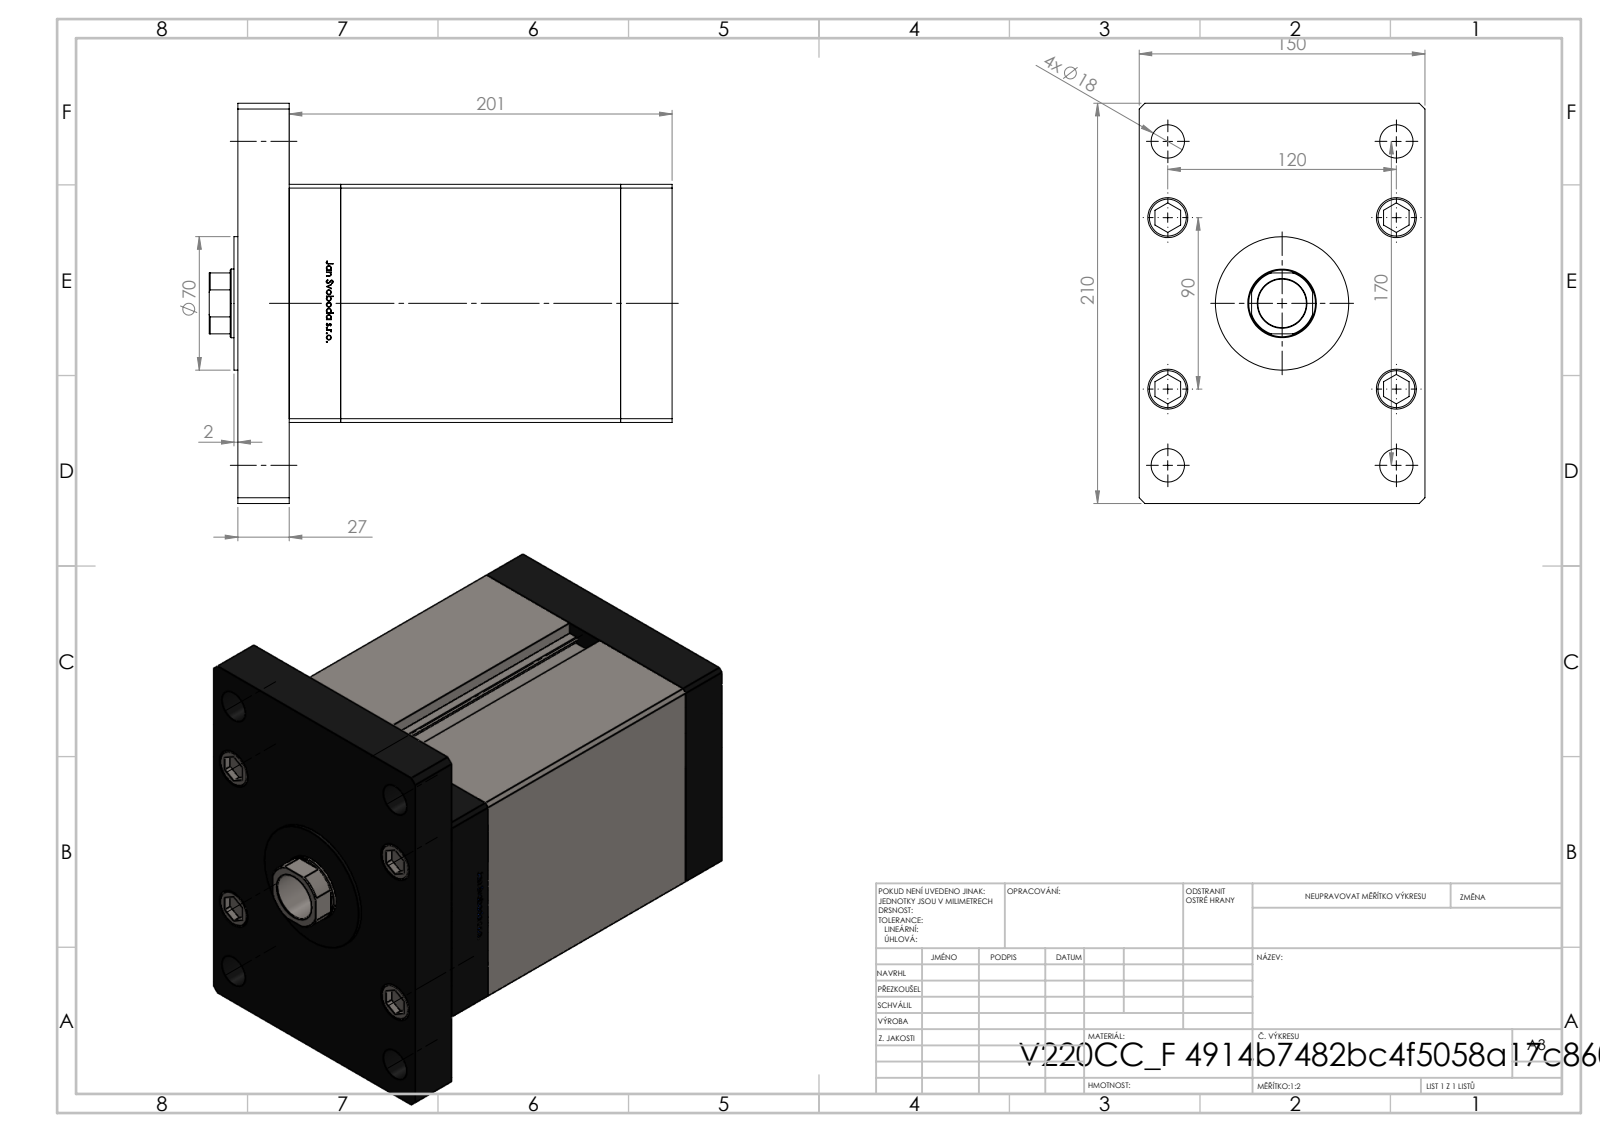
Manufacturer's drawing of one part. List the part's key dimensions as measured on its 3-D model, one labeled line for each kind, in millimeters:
Part name (STEP PRODUCT): V220C_F_MIDDLE; V220C_VC_F; V220C_FRONT_F; ALLEN BOLT (+2 more)
STEP written by: SolidWorks 2019 (CONFIG_CONTROL_DESIGN)
Units: millimetres
Bodies: 19 solids, 1298 faces (513 planar, 179 cylindrical, 606 other)
Overall size (bounding box): 243 × 210 × 150
Volume: 4 076 000 mm³ · Surface area: 452 115 mm²
Round holes (diameter × count): ⌀17.5 ×9, ⌀22 ×5, ⌀16 ×4, ⌀21 ×4, ⌀25.5 ×1, ⌀36 ×1, ⌀37.5 ×1
Round bosses / shafts (diameter × count): ⌀8 ×9, ⌀21 ×5, ⌀80 ×1, ⌀70 ×1
Partial cylindrical surfaces — rounded edges, fillets, slot ends (radius × count): R0.93 ×2, R17.5 ×1
Main face-to-face distances: 27, 174, 201, 150, 147, 54, 125, 167.5, 228, 33.5
Hole centre spacings: 51, 40, 75, 104.04, 120, 126.49, 130, 176.92
